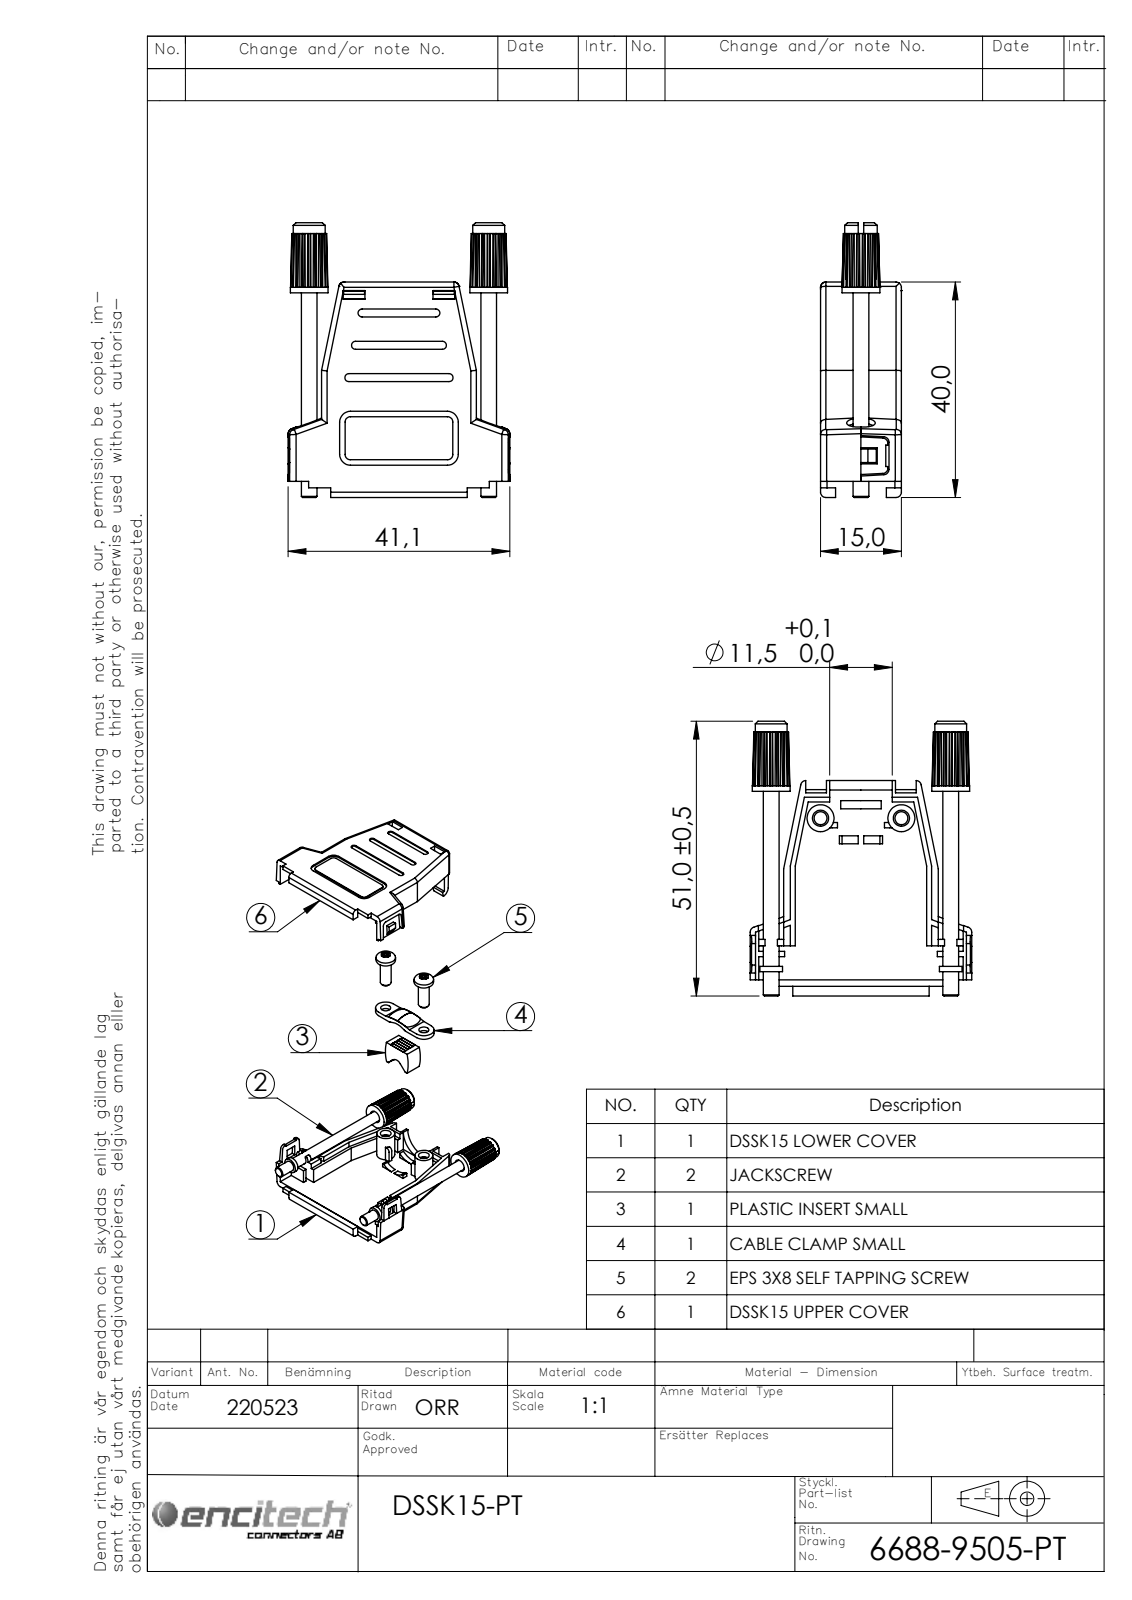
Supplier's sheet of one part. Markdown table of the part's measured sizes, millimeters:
| quantity | value |
| --- | --- |
| part name | 6811-0162-13 Part 2; 6830-0106-01; 6855-0109-01; 6688-9505-PT (+3 more) |
| STEP written by | SolidWorks 2021 (AUTOMOTIVE_DESIGN) |
| units | millimeters |
| bodies | 10 solids, 1058 faces (726 planar, 233 cylindrical, 99 other) |
| overall size | 51 × 41.1 × 15 |
| volume | 8 231 mm³ |
| surface area | 11 781 mm² |
| round holes (diameter × count) | 2.4 × 2, 2.8 × 2, 3 × 2, 0.75 × 1, 0.9 × 1, 1.25 × 1, 2.5 × 1, 3.5 × 1, 11.6 × 1 |
| round bosses / shafts (diameter × count) | 7 × 2, 6 × 2, 5.45 × 2, 5 × 2, 4.2 × 2, 2.9 × 2 |
| partial cylindrical surfaces (radius × count) | 1 × 32, 0.25 × 24, 0.5 × 20, 0.12 × 16, 0.75 × 6, 2 × 6, 0.4 × 4, 1.2 × 4 |
| main face-to-face distances | 1.7, 13.3, 11.6, 15, 7.5, 5.8, 7.3, 2, 1.2, 1.5 |
| hole center spacings | 7.54, 7.8, 8.2, 9.26, 9.3, 11.75, 12.73, 15 |
